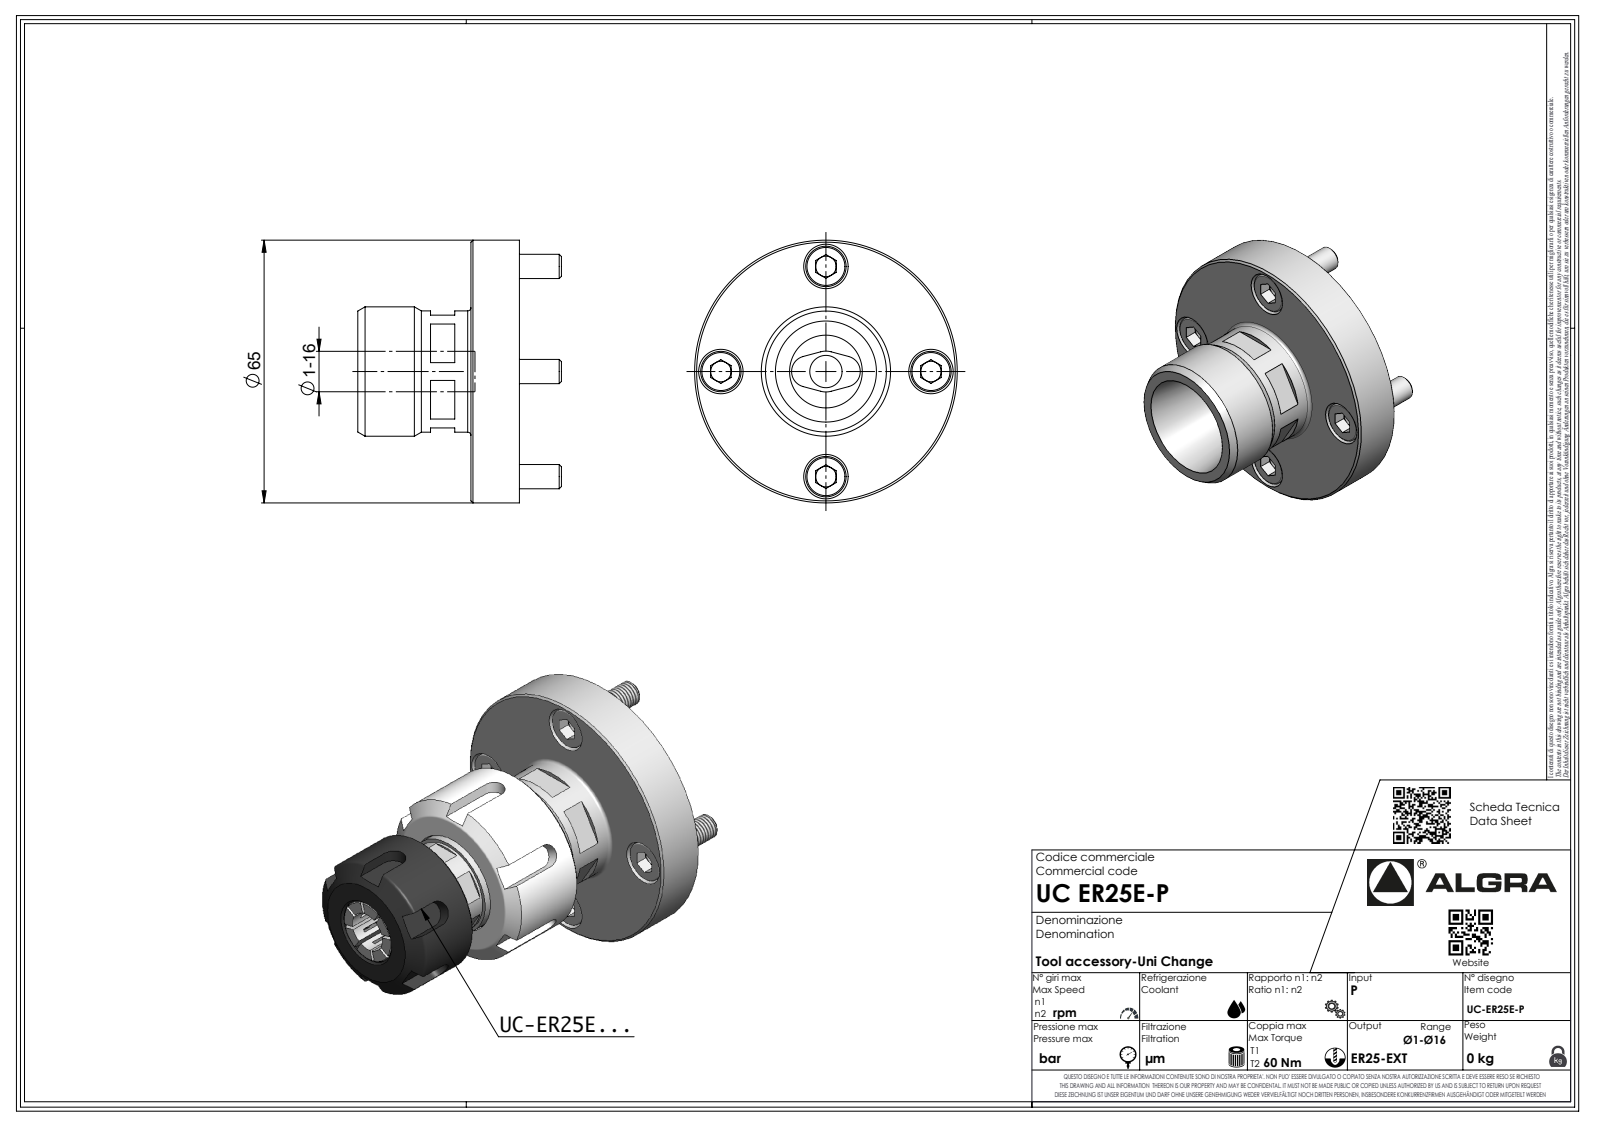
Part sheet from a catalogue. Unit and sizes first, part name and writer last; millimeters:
Units: millimetres
Overall size (bounding box): 65 × 65 × 50.4
Round holes (diameter × count): ⌀6.6 ×4, ⌀11 ×4, ⌀8 ×1, ⌀40 ×1
Round bosses / shafts (diameter × count): ⌀10 ×4, ⌀6 ×4, ⌀65 ×1, ⌀32 ×1, ⌀30 ×1
Main face-to-face distances: 12, 0.5, 11.5, 40, 39.5, 28, 27.9, 11.6, 11.1, 0.4
Hole centre spacings: 26, 36.77, 52
Bodies: 0 solids, 111 faces (72 planar, 21 cylindrical, 18 other)
Part name (STEP PRODUCT): UC-ER25E-P
STEP written by: SolidWorks 2016 (AUTOMOTIVE_DESIGN)
